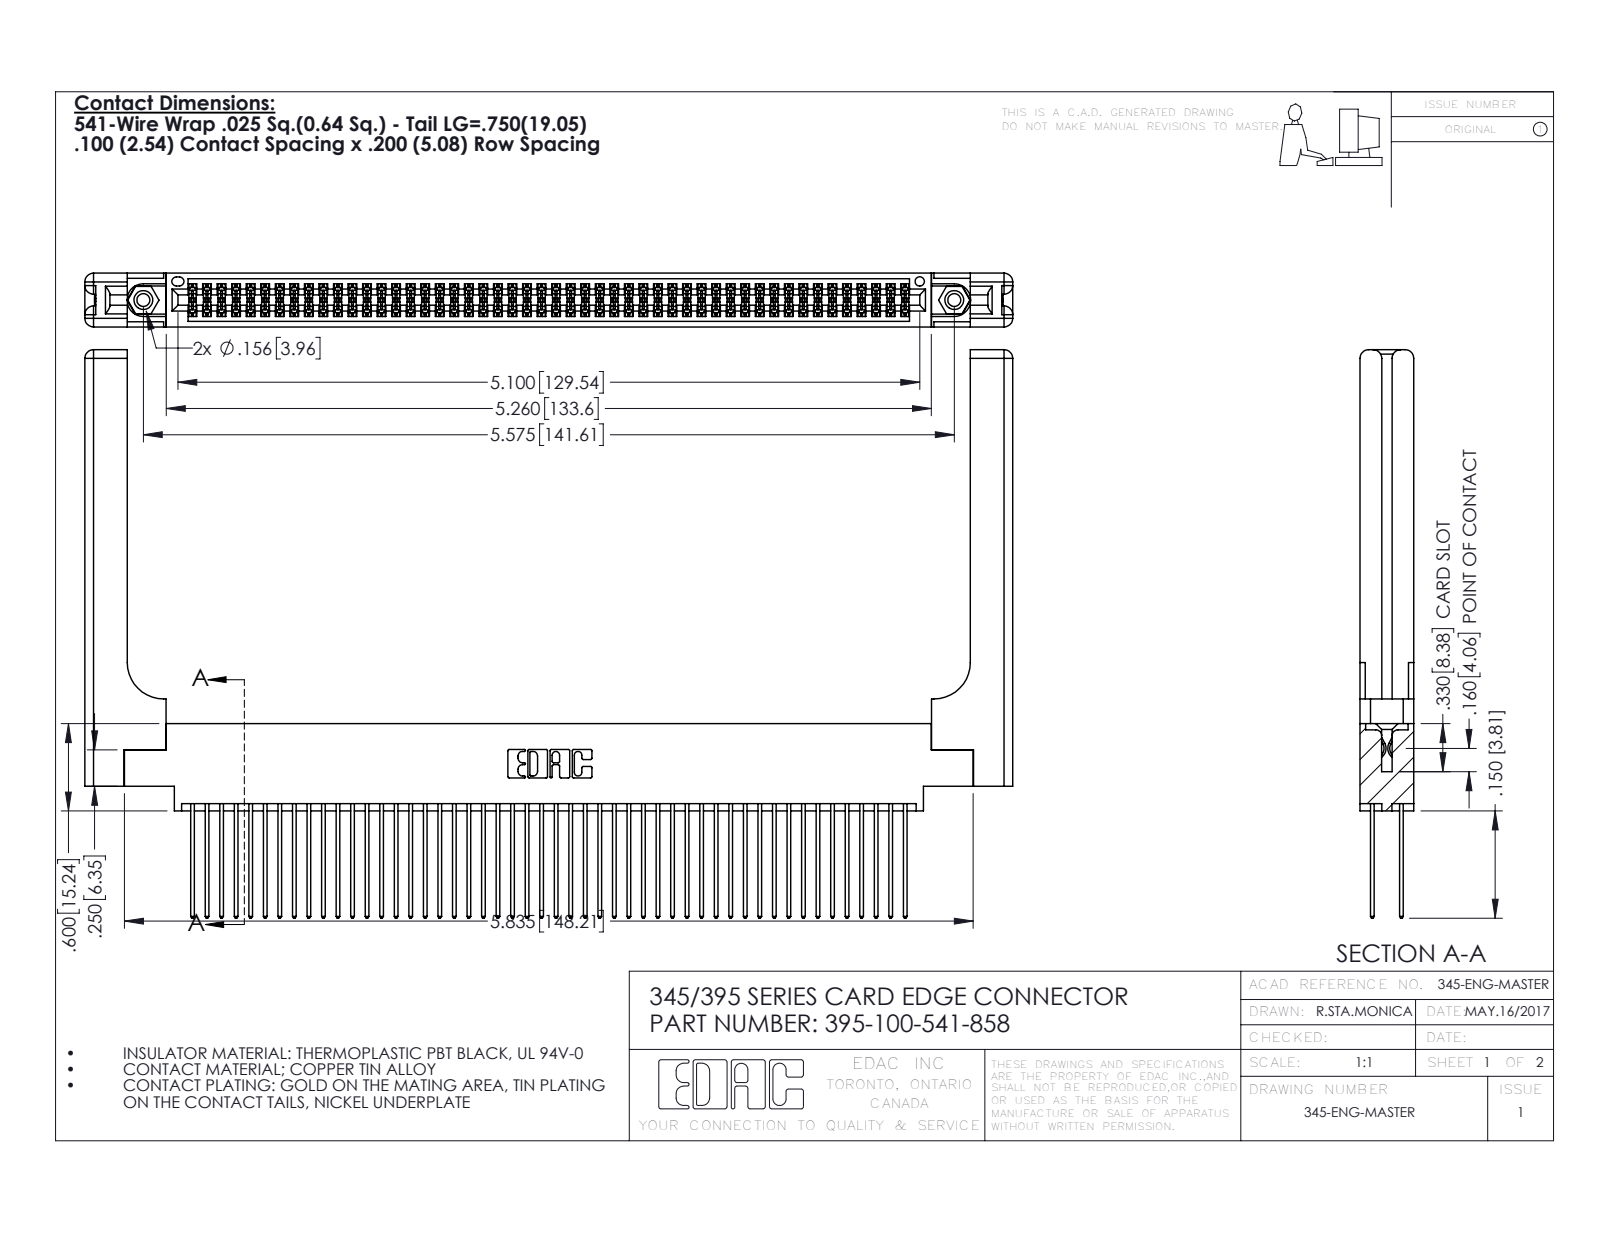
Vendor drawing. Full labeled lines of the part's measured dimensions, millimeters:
Part name (STEP PRODUCT): 345-220-058_345-220-058; 345-250-001_345-250-001-102; 345 Part_0.170 Offset - 0.156 Dia-TH; 345-292-001_345-293-141 (+1 more)
STEP written by: SolidWorks 2016 (CONFIG_CONTROL_DESIGN)
Units: millimetres
Bodies: 105 solids, 5386 faces (3532 planar, 1794 cylindrical, 60 other)
Overall size (bounding box): 162 × 99.2 × 9.4
Volume: 24 740 mm³ · Surface area: 32 110 mm²
Round holes (diameter × count): ⌀2.3 ×2, ⌀3.2 ×2, ⌀4 ×2, ⌀1.6 ×1
Round bosses / shafts (diameter × count): ⌀3.9 ×2
Partial cylindrical surfaces — rounded edges, fillets, slot ends (radius × count): R0.2 ×150, R0.3 ×100, R0.3 ×22, R1.5 ×16, R0.2 ×6, R0.8 ×6, R0.7 ×3, R0.4 ×2
Main face-to-face distances: 1.8, 7.6, 9.4, 2.5, 6.9, 0.6, 5.1, 5.7, 4.4, 3.8
Hole centre spacings: 6.9, 135.6, 141.6
